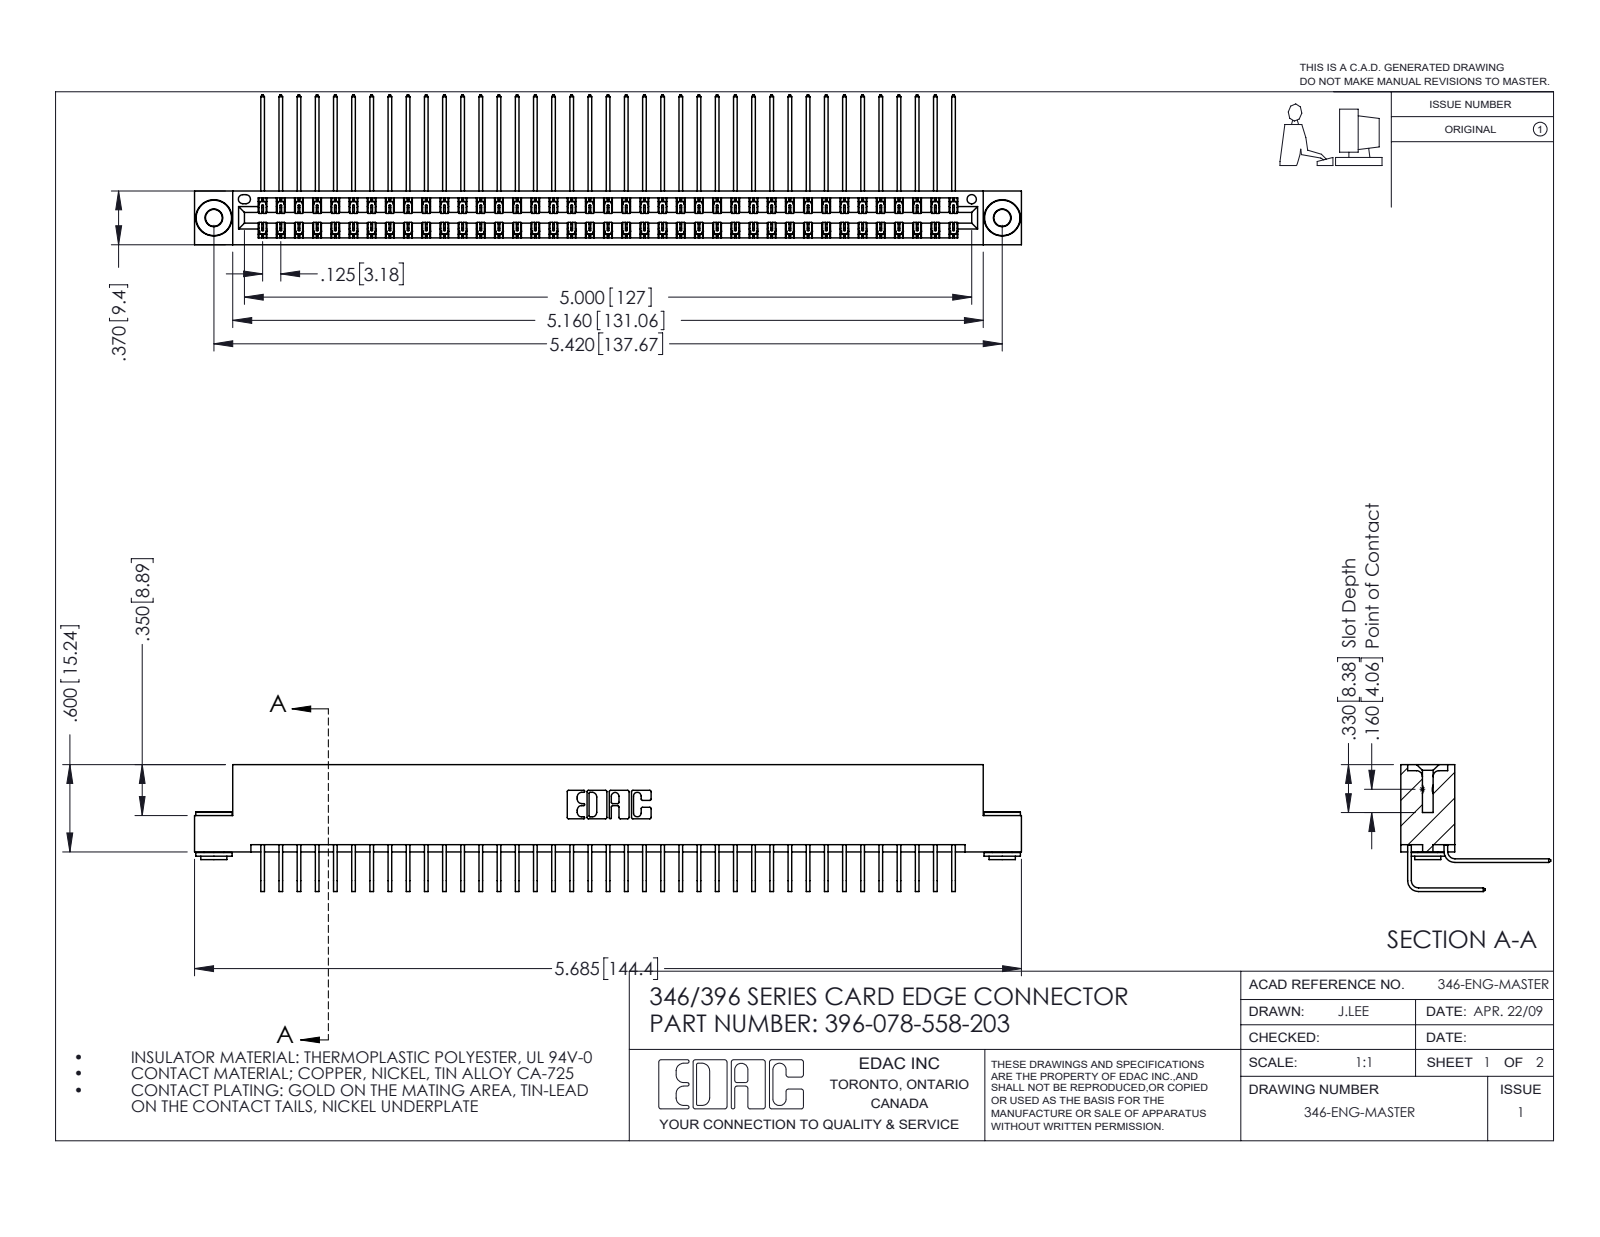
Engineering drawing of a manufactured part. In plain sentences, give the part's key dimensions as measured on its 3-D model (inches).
The part is named "396-078-558-203; 345-250-002_345-250-002-102; 345-292-001_558 559 Tail - 1; 346 Part_Flush Mounting Lugs - 0.156 Dia-TH (+1 more)". Its 3-D file was written by "SolidWorks 2016 (CONFIG_CONTROL_DESIGN)". It is 81 solids with 4372 faces: 2972 planar, 1392 cylindrical and 8 other. Overall it measures 5.685 by 1.03 by 0.873 inches. Its volume is 0.886 cubic inches and its surface area 34.56 square inches. Round holes: 2 of diameter 0.116, 2 of diameter 0.156, 1 of diameter 0.064. Round bosses or shafts: 2 of diameter 0.25, 2 of diameter 0.18, 2 of diameter 0.136. Partial cylindrical surfaces (rounded edges, fillets, slot ends): 117 of radius 0.006, 22 of radius 0.01, 6 of radius 0.007, 6 of radius 0.031, 3 of radius 0.026, 2 of radius 0.014, 2 of radius 0.022, 2 of radius 0.024. The main face-to-face distances are 0.322, 0.048, 0.025, 0.25, 0.37, 0.298, 0.072, 0.275, 0.148, 0.222. The hole center spacings are 0.246, 5.211, 5.42.
